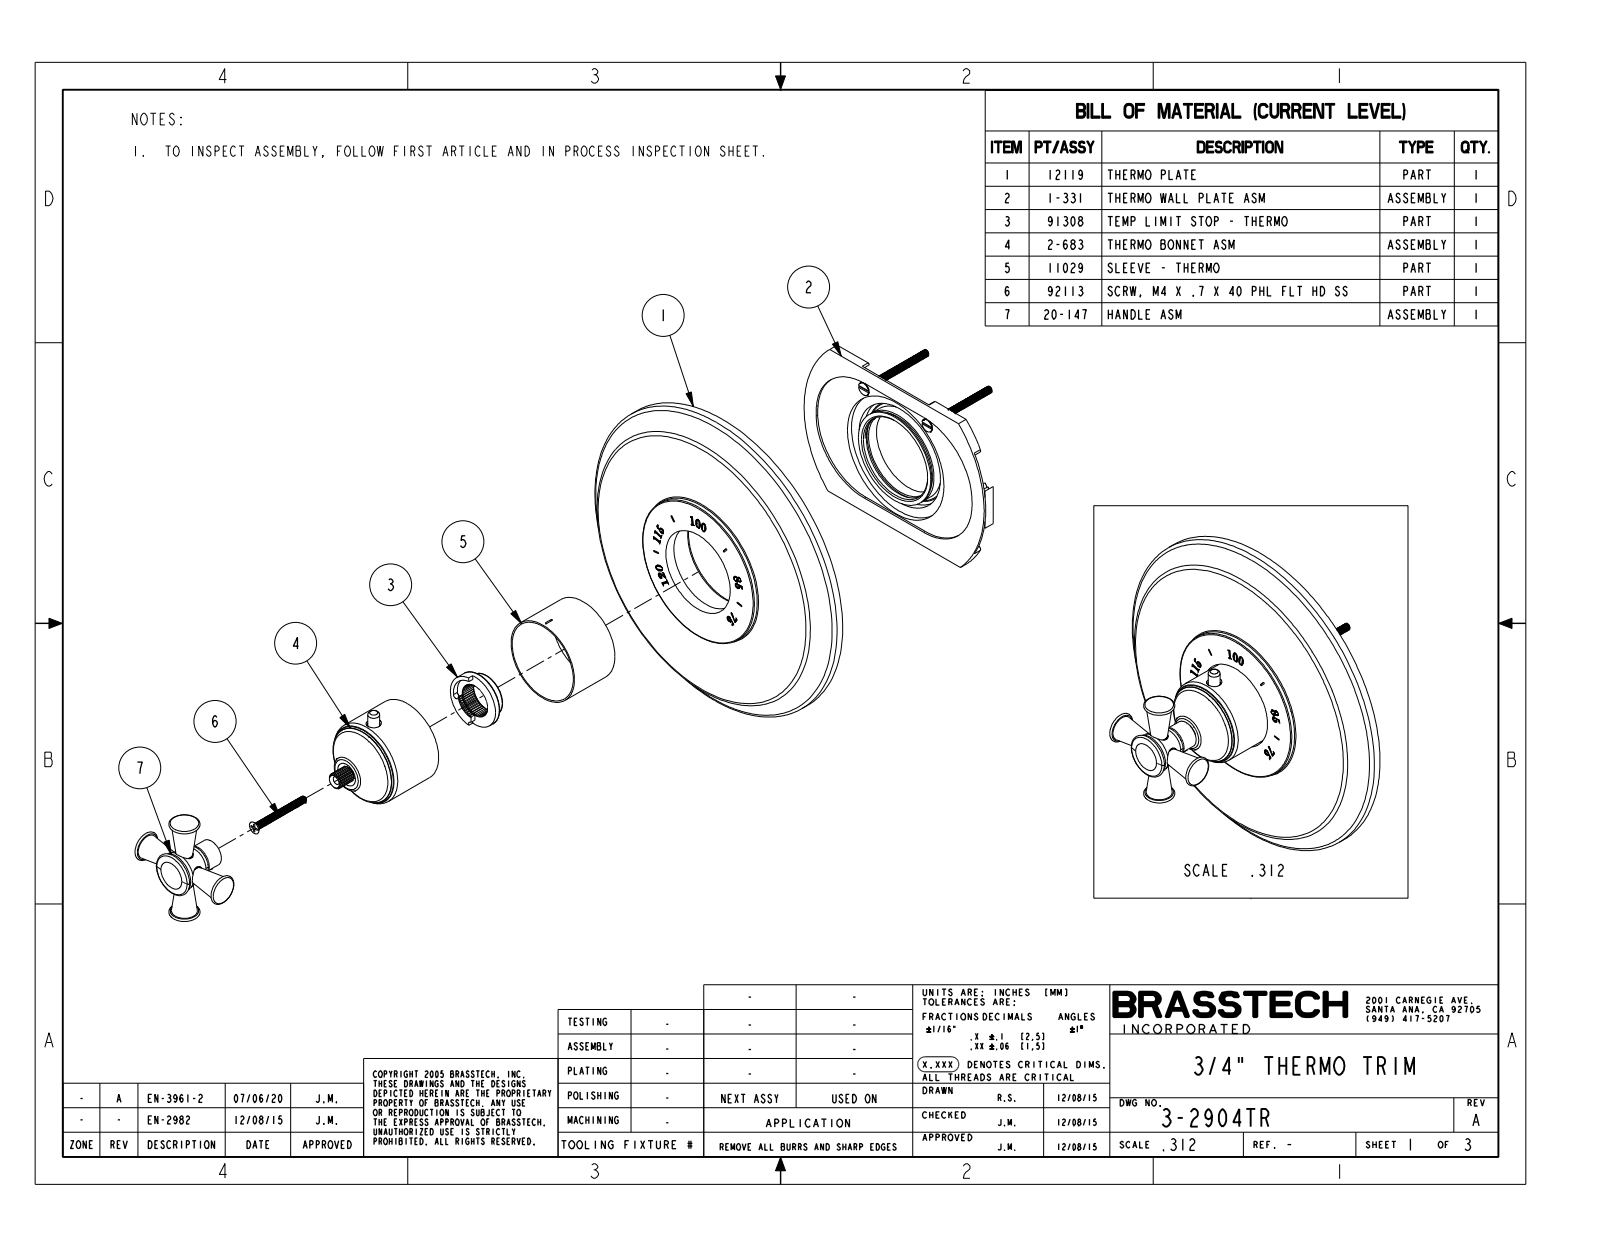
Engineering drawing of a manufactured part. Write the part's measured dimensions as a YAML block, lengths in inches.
part_name: "3-2904TR"
step_written_by: "CREO PARAMETRIC BY PTC INC, 2018400 (CONFIG_CONTROL_DESIGN)"
units: inches
bodies: {solids: 1, faces: 110, planar: 14, cylindrical: 10, other: 86}
overall_size: [7.5, 7.5, 3.558]
volume: 30.59
surface_area: 115.9
round_bosses_or_shafts:
  - {diameter: 7.5, count: 1}
  - {diameter: 1.94, count: 1}
  - {diameter: 0.625, count: 1}
  - {diameter: 0.4, count: 1}
  - {diameter: 0.26, count: 1}
face_to_face_distances: [0.625, 0.75, 0.125, 2.254, 1.629, 1.504, 2.284, 1.659, 1.534, 0.03]
